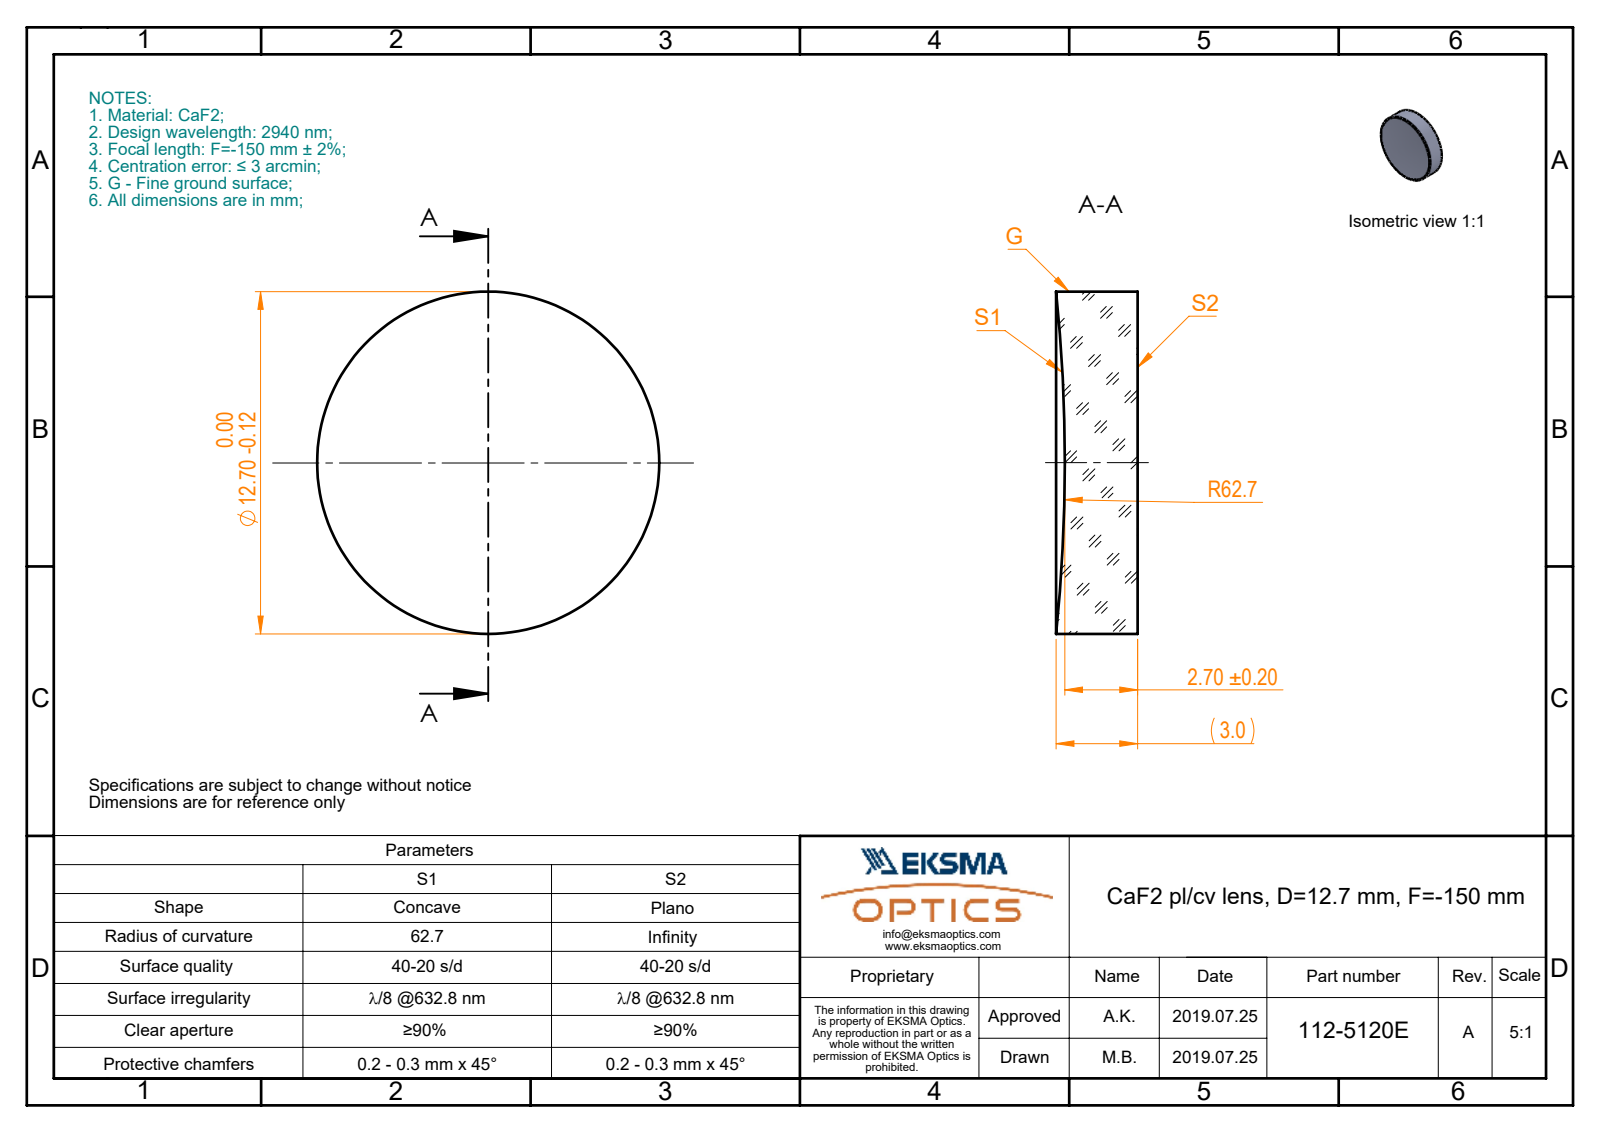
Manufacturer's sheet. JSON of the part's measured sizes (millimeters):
{"part_name": "112-5120E CaF2 pl-cv 12.7 F-150", "step_written_by": "SolidWorks 2017 (CONFIG_CONTROL_DESIGN)", "units": "millimeters", "bodies": {"solids": 1, "faces": 5, "planar": 1, "cylindrical": 2, "other": 2}, "overall_size": [12.7, 12.7, 3.02], "volume_mm3": 362, "surface_area_mm2": 374, "round_bosses_or_shafts": [[12.7, 1]]}
